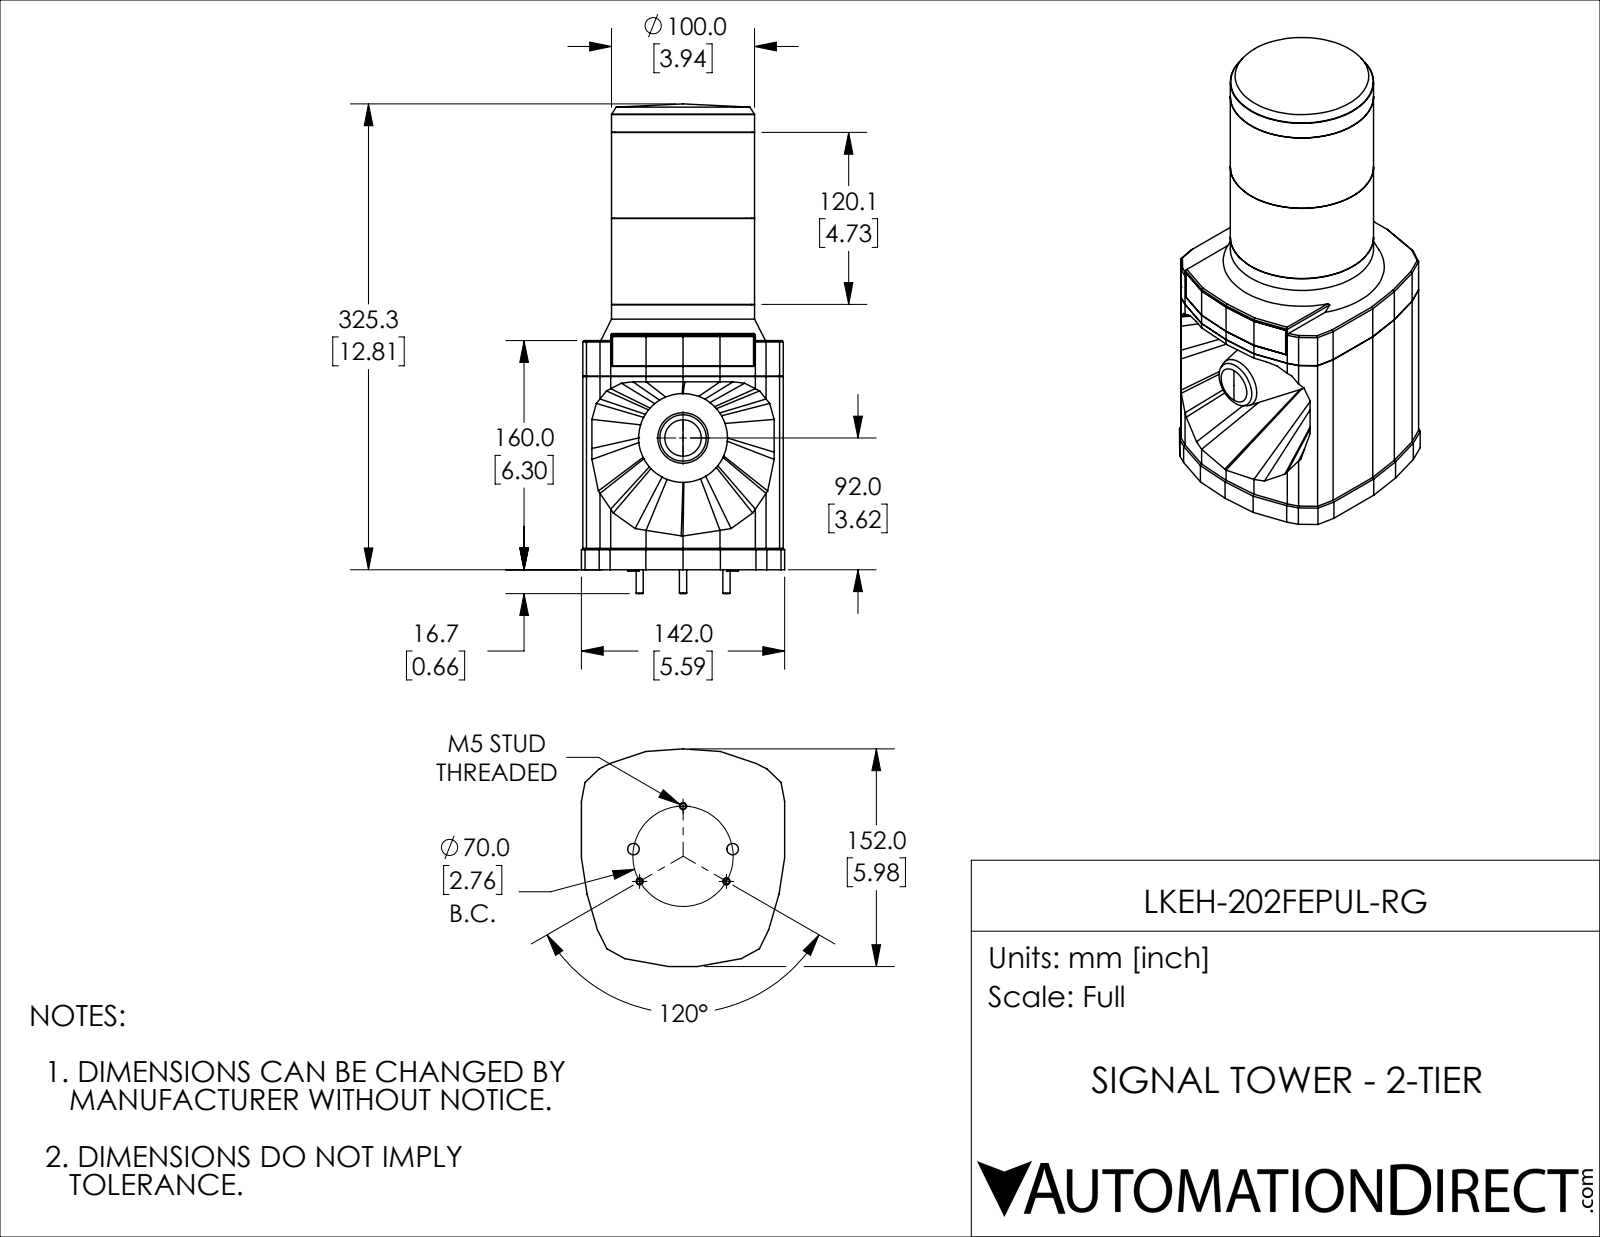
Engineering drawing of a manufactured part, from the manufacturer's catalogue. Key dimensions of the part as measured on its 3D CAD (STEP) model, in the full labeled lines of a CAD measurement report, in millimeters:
Part name (STEP PRODUCT): LKEH-202FEPUL-RG
STEP written by: SolidWorks 2018 (AUTOMOTIVE_DESIGN)
Units: millimetres
Bodies: 1 solid, 268 faces (182 planar, 24 cylindrical, 62 other)
Overall size (bounding box): 342 × 152 × 142
Volume: 3 799 000 mm³ · Surface area: 196 000 mm²
Round bosses / shafts (diameter × count): ⌀5 ×3, ⌀8 ×2, ⌀100 ×1, ⌀95.6 ×1
Main face-to-face distances: 1, 140, 160, 165, 5, 60.1, 60, 60.2, 141, 50.1
